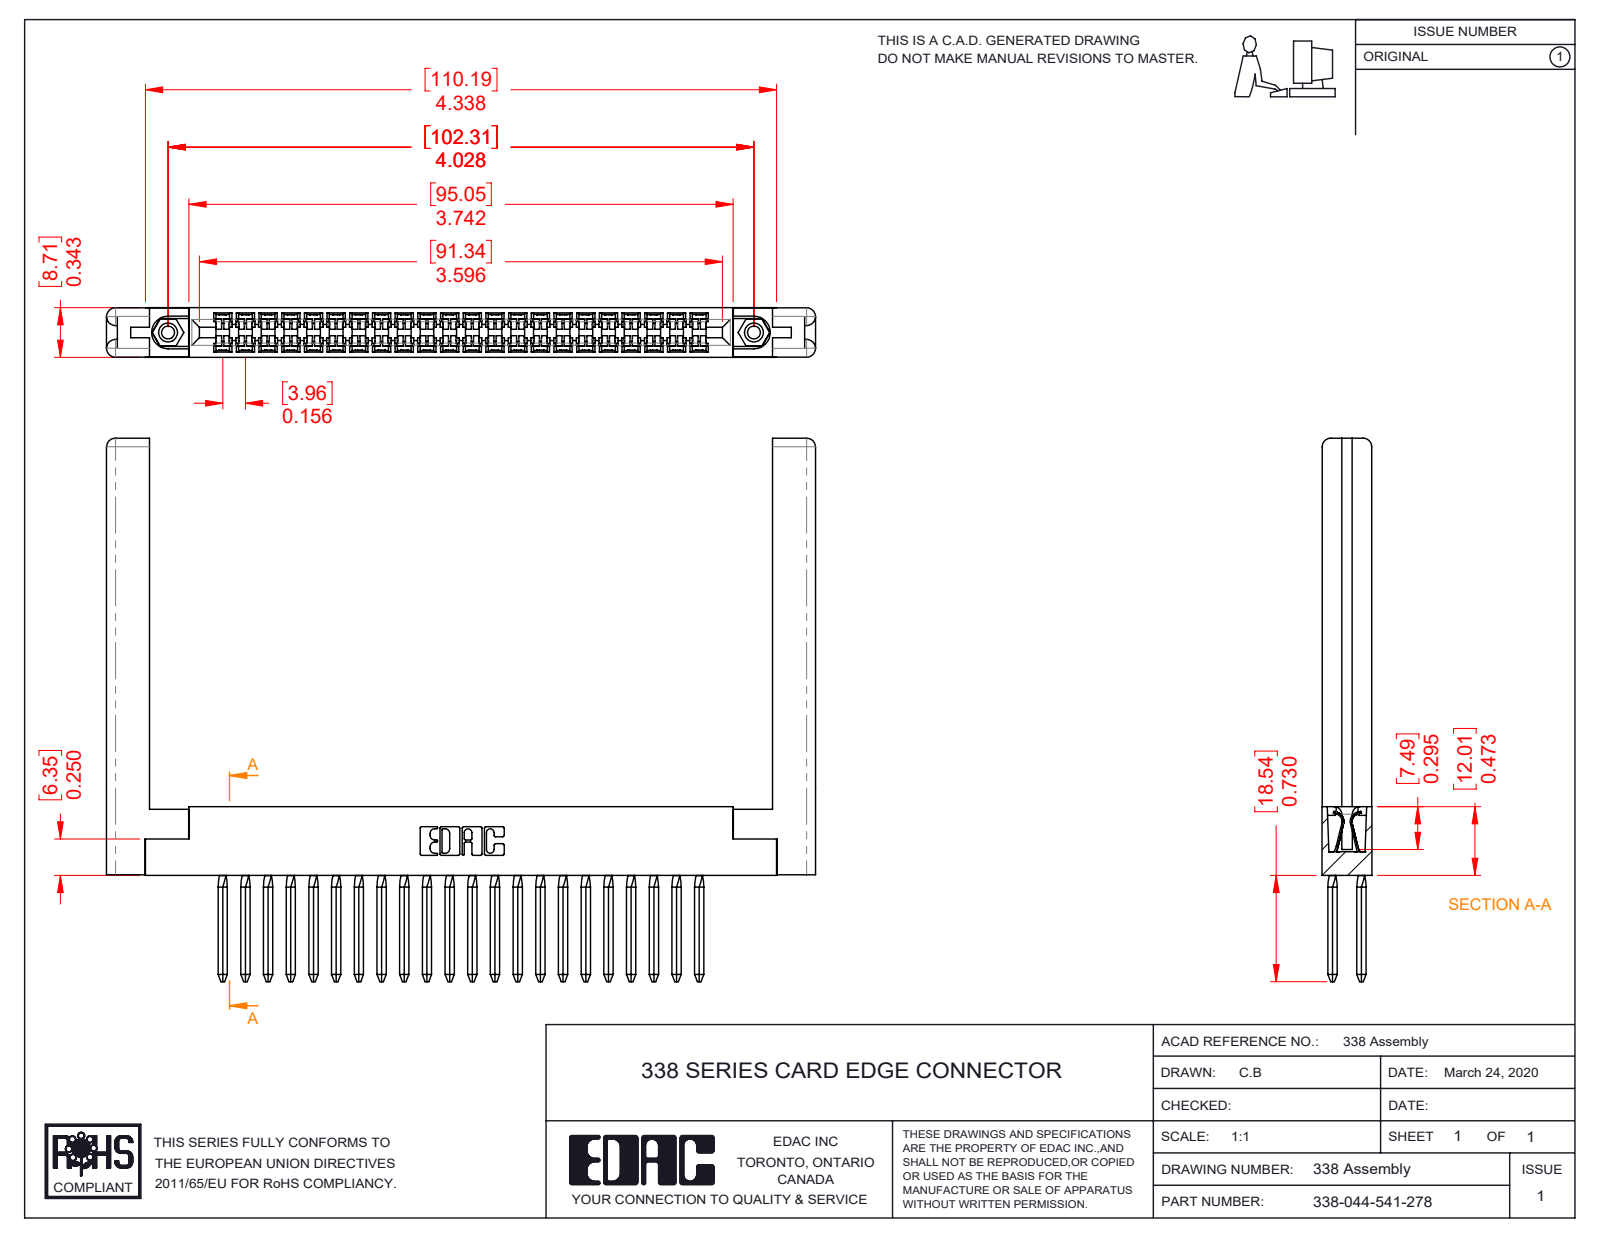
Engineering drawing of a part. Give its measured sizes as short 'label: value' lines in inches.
name: 307-220-058; 338-210-001_338-210-022-004; 338-290-001_541; 345-250-001_345-250-001-102 (+1 more)
written by: SolidWorks 2016 (CONFIG_CONTROL_DESIGN)
unit: in
bodies: 49 solids, 3184 faces (2202 planar, 782 cylindrical, 200 other)
size: 4.874 × 3.735 × 0.343
volume: 1.04 in³; area: 34.59 in²
holes: 2× ⌀0.089, 2× ⌀0.125, 2× ⌀0.156
bosses: 2× ⌀0.155
rounds: 134× R0.025, 44× R0.008, 36× R0.055, 36× R0.067, 35× R0.1, 22× R0.01, 8× R0.061, 6× R0.007
face distances: 0.341, 0.343, 0.34, 0.136, 0.207, 0.134, 0.206, 0.22, 4.284, 0.071
hole spacings: 4.028
